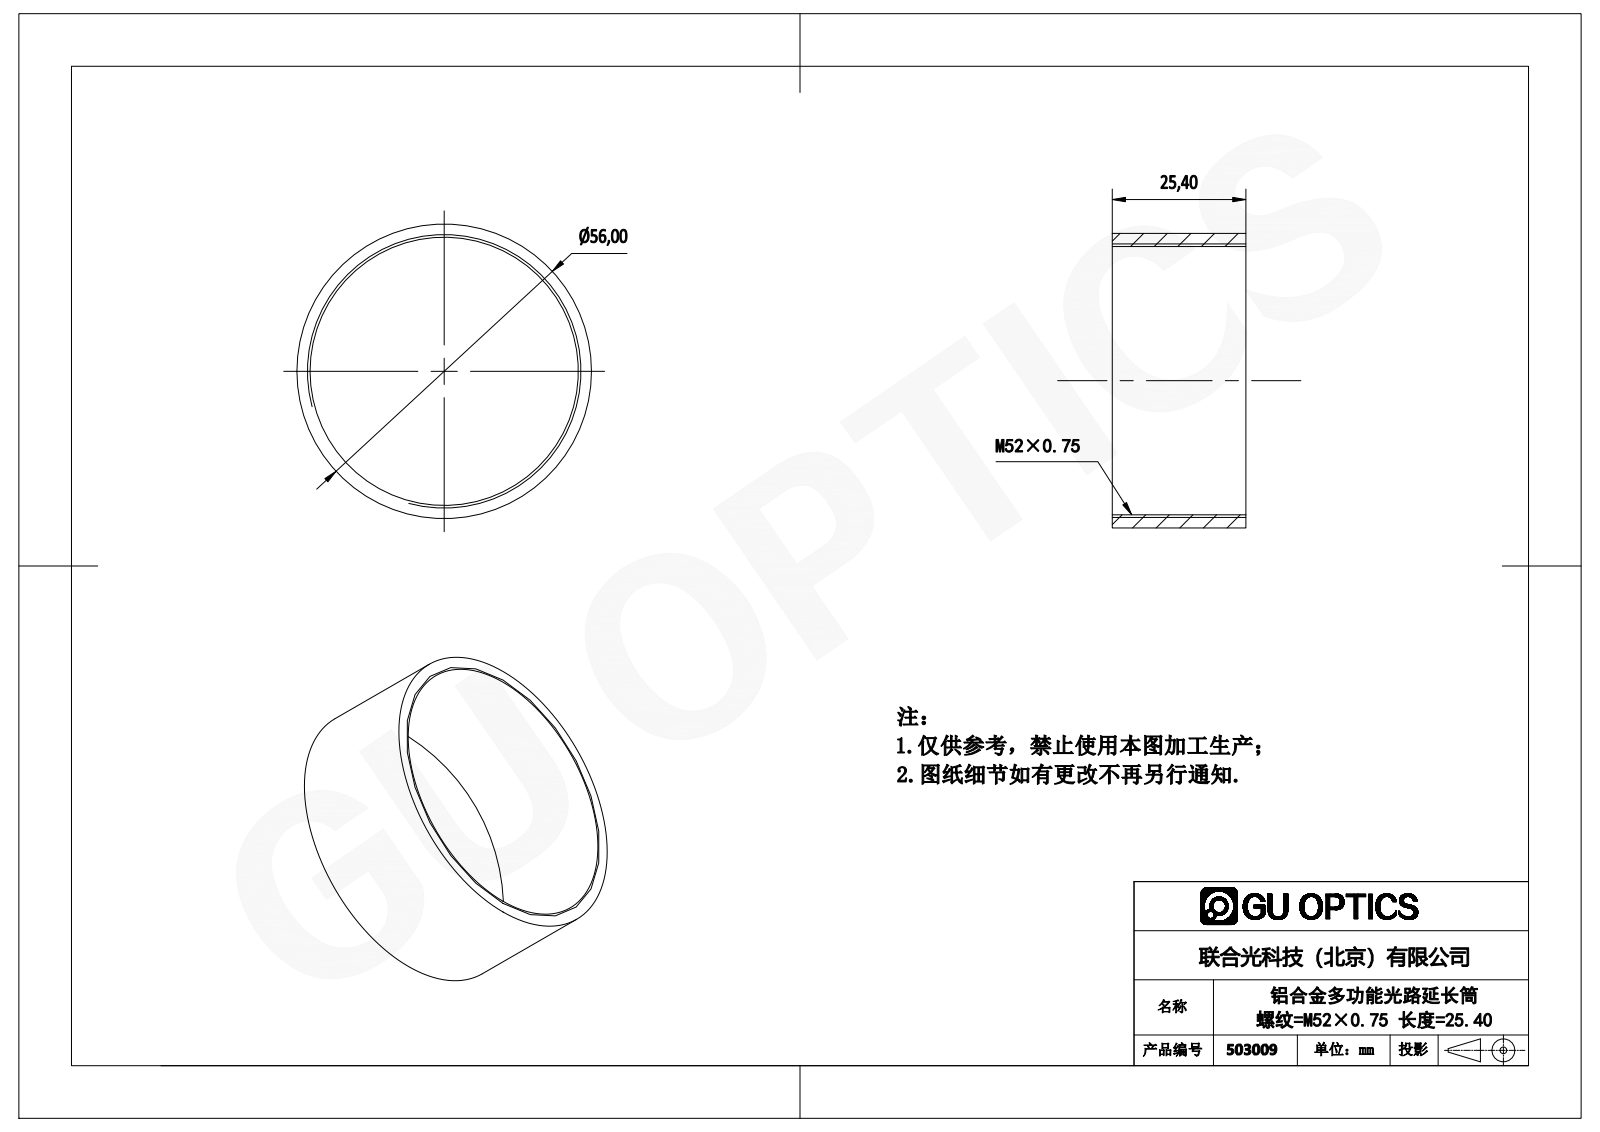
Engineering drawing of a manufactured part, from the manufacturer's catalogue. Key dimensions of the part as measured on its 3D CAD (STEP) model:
Part name (STEP PRODUCT): 503009
STEP written by: SolidWorks 2016 (AUTOMOTIVE_DESIGN)
Units: millimetres
Bodies: 1 solid, 6 faces (2 planar, 4 cylindrical, 0 other)
Overall size (bounding box): 56 × 56 × 25.4
Volume: 10 673 mm³ · Surface area: 9 379 mm²
Round holes (diameter × count): ⌀51 ×1
Round bosses / shafts (diameter × count): ⌀56 ×1
Main face-to-face distances: 25.4
